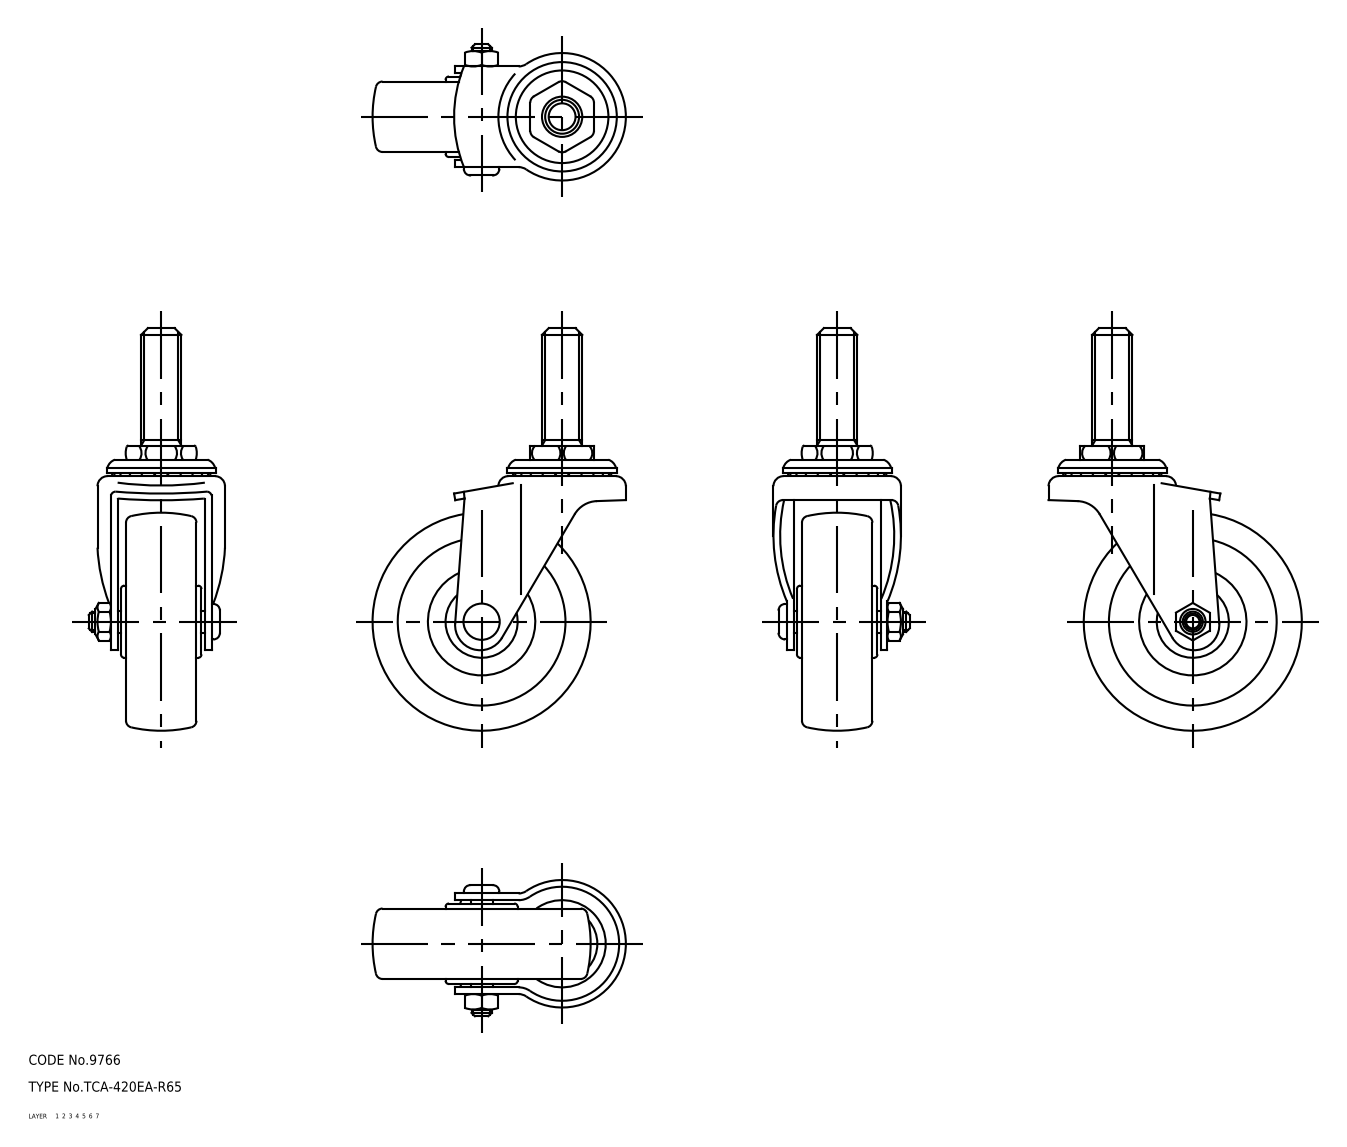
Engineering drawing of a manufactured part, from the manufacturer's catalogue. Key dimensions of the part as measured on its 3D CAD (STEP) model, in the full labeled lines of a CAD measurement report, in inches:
Part name (STEP PRODUCT): 67132833; 67132846; 67132859; 67132872 (+1 more)
STEP written by: CADfix (AUTOMOTIVE_DESIGN)
Units: inches
Bodies: 5 solids, 221 faces (0 planar, 0 cylindrical, 221 other)
Overall size (bounding box): 4.724 × 2.972 × 1.598
Volume: 5.2 in³ · Surface area: 42.01 in²
